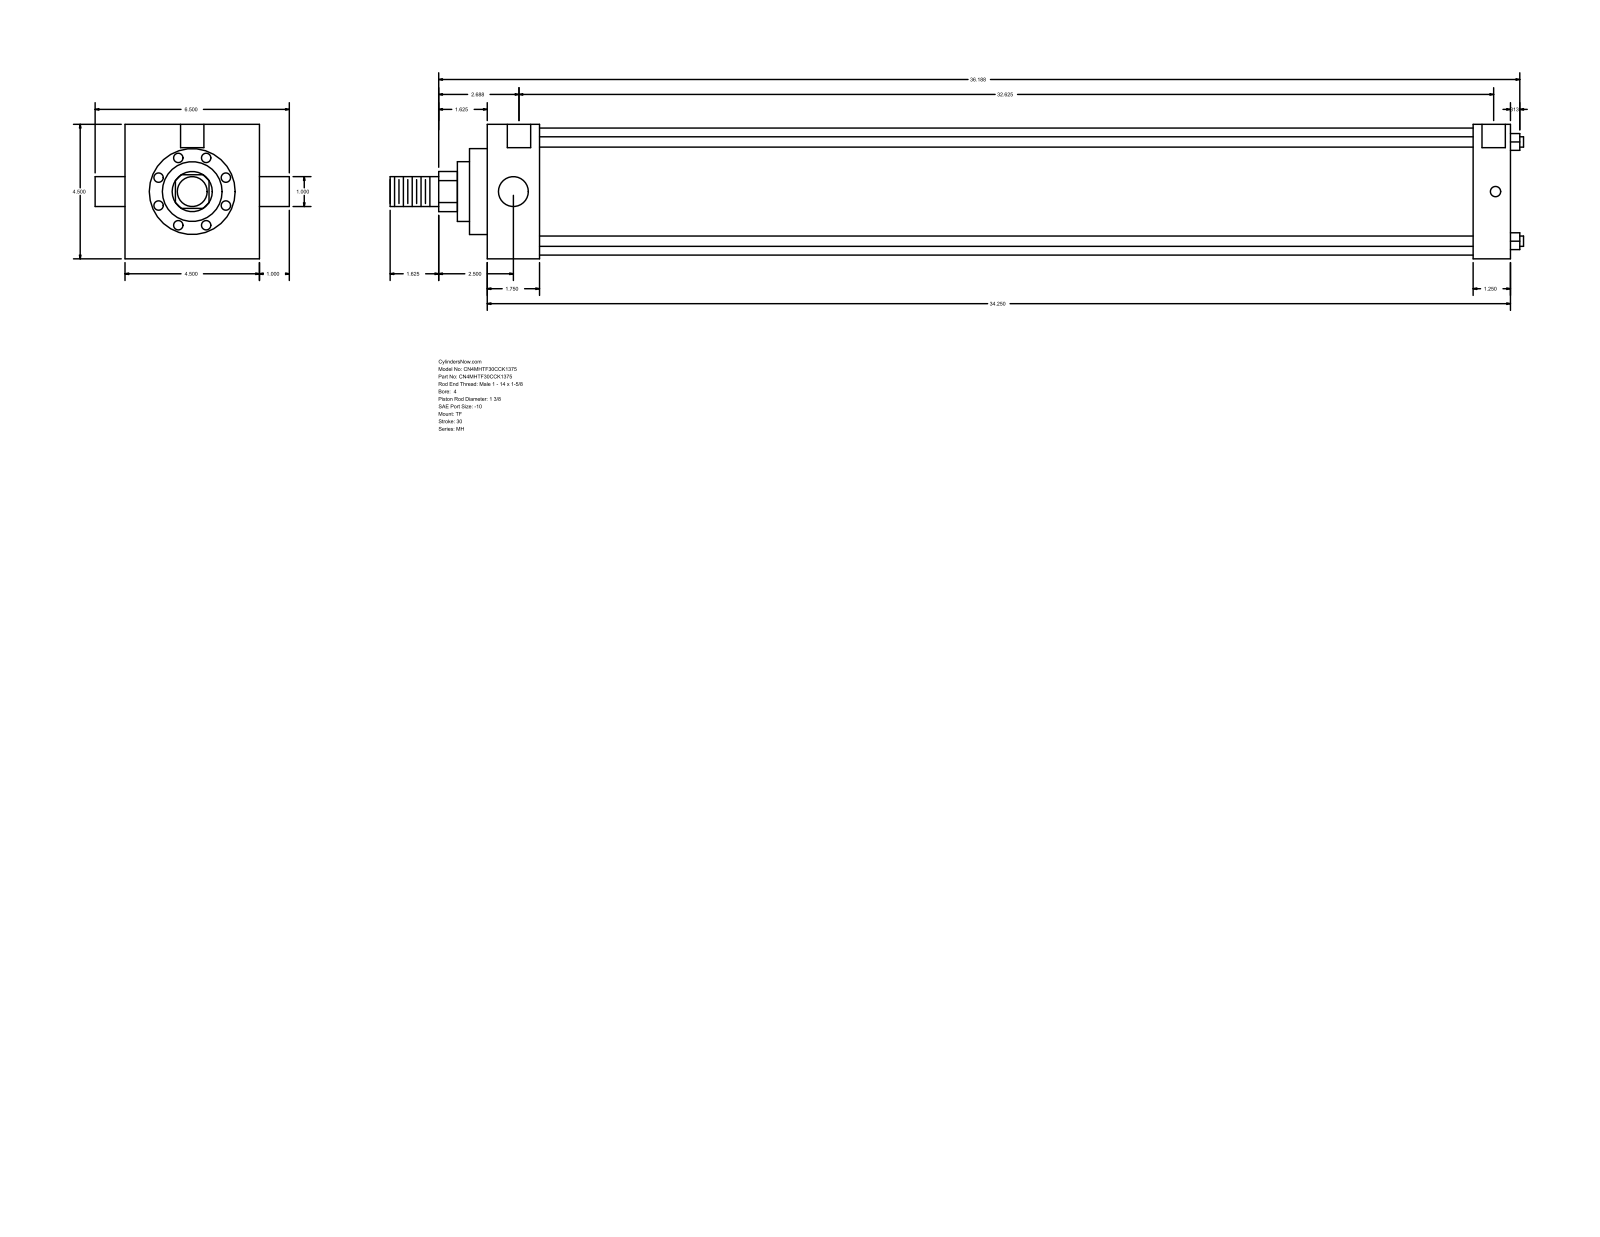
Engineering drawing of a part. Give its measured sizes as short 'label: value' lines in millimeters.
name: MH_TF__0400_1.375
written by: GSSL Pune (CONFIG_CONTROL_DESIGN)
unit: mm
bodies: 0 solids, 86 faces (61 planar, 25 cylindrical, 0 other)
size: 963.61 × 165.1 × 114.3
holes: 3× ⌀8.73, 2× ⌀19.84
bosses: 4× ⌀8.76, 2× ⌀25.4, 1× ⌀107.95, 1× ⌀73.03, 1× ⌀50.8, 1× ⌀34.92
rounds: 1× R17.06
face distances: 114.3, 869.96, 44.45, 825.51, 838.21, 793.76, 31.75, 15.08, 59.53, 853.29
hole spacings: 1.58, 1.59, 828.68, 830.26, 830.27, 831.85
